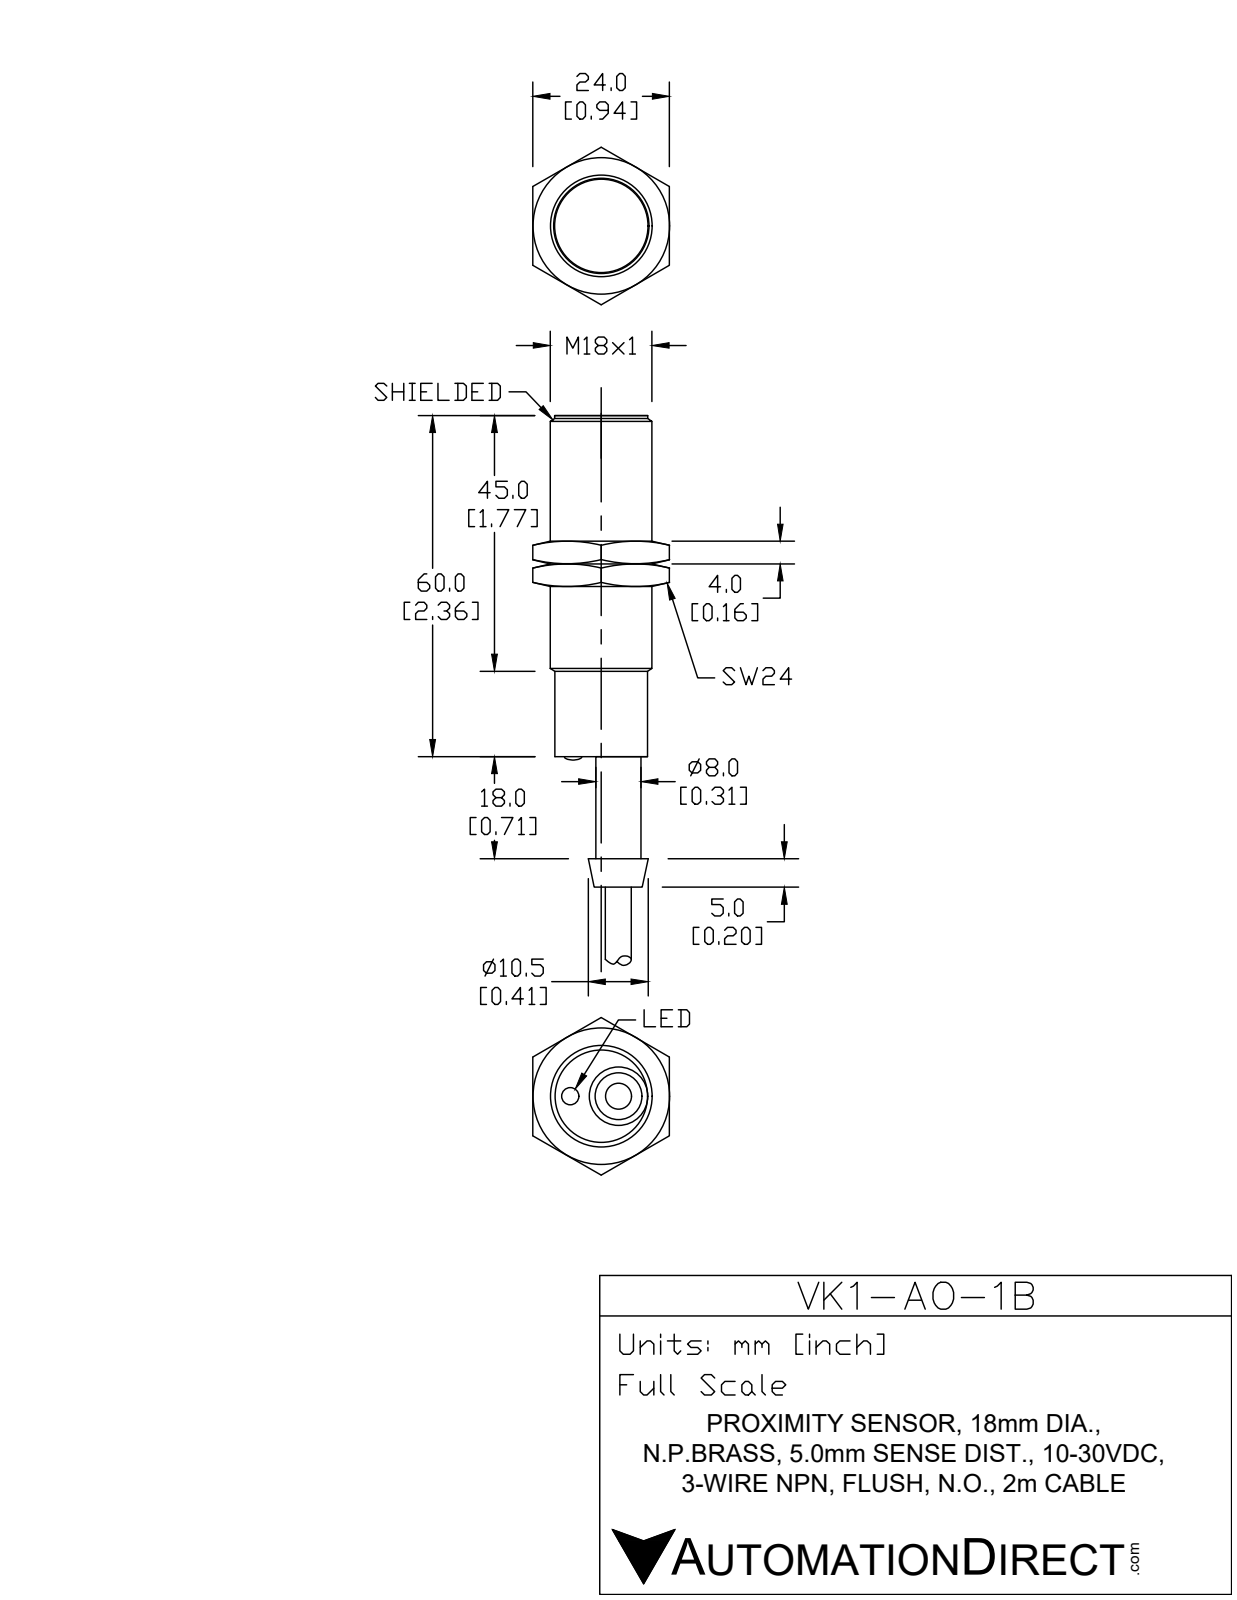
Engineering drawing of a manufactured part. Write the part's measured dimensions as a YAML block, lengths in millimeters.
part_name: "VK1-A0-1B"
step_written_by: "SolidWorks 2017 (AUTOMOTIVE_DESIGN)"
units: millimeters
bodies: {solids: 4, faces: 43, planar: 14, cylindrical: 15, other: 14}
overall_size: [112, 18, 18]
volume: 16300
surface_area: 5812
round_holes:
  - {diameter: 4.7, count: 1}
round_bosses_or_shafts:
  - {diameter: 18, count: 1}
  - {diameter: 16.5, count: 1}
  - {diameter: 16.4, count: 1}
  - {diameter: 10.4, count: 1}
  - {diameter: 8, count: 1}
partial_cylinders:
  - {radius: 8.1, count: 1}
face_to_face_distances: [49.5, 0.5, 50, 60, 59.5, 10, 72, 71.5, 22, 12]
